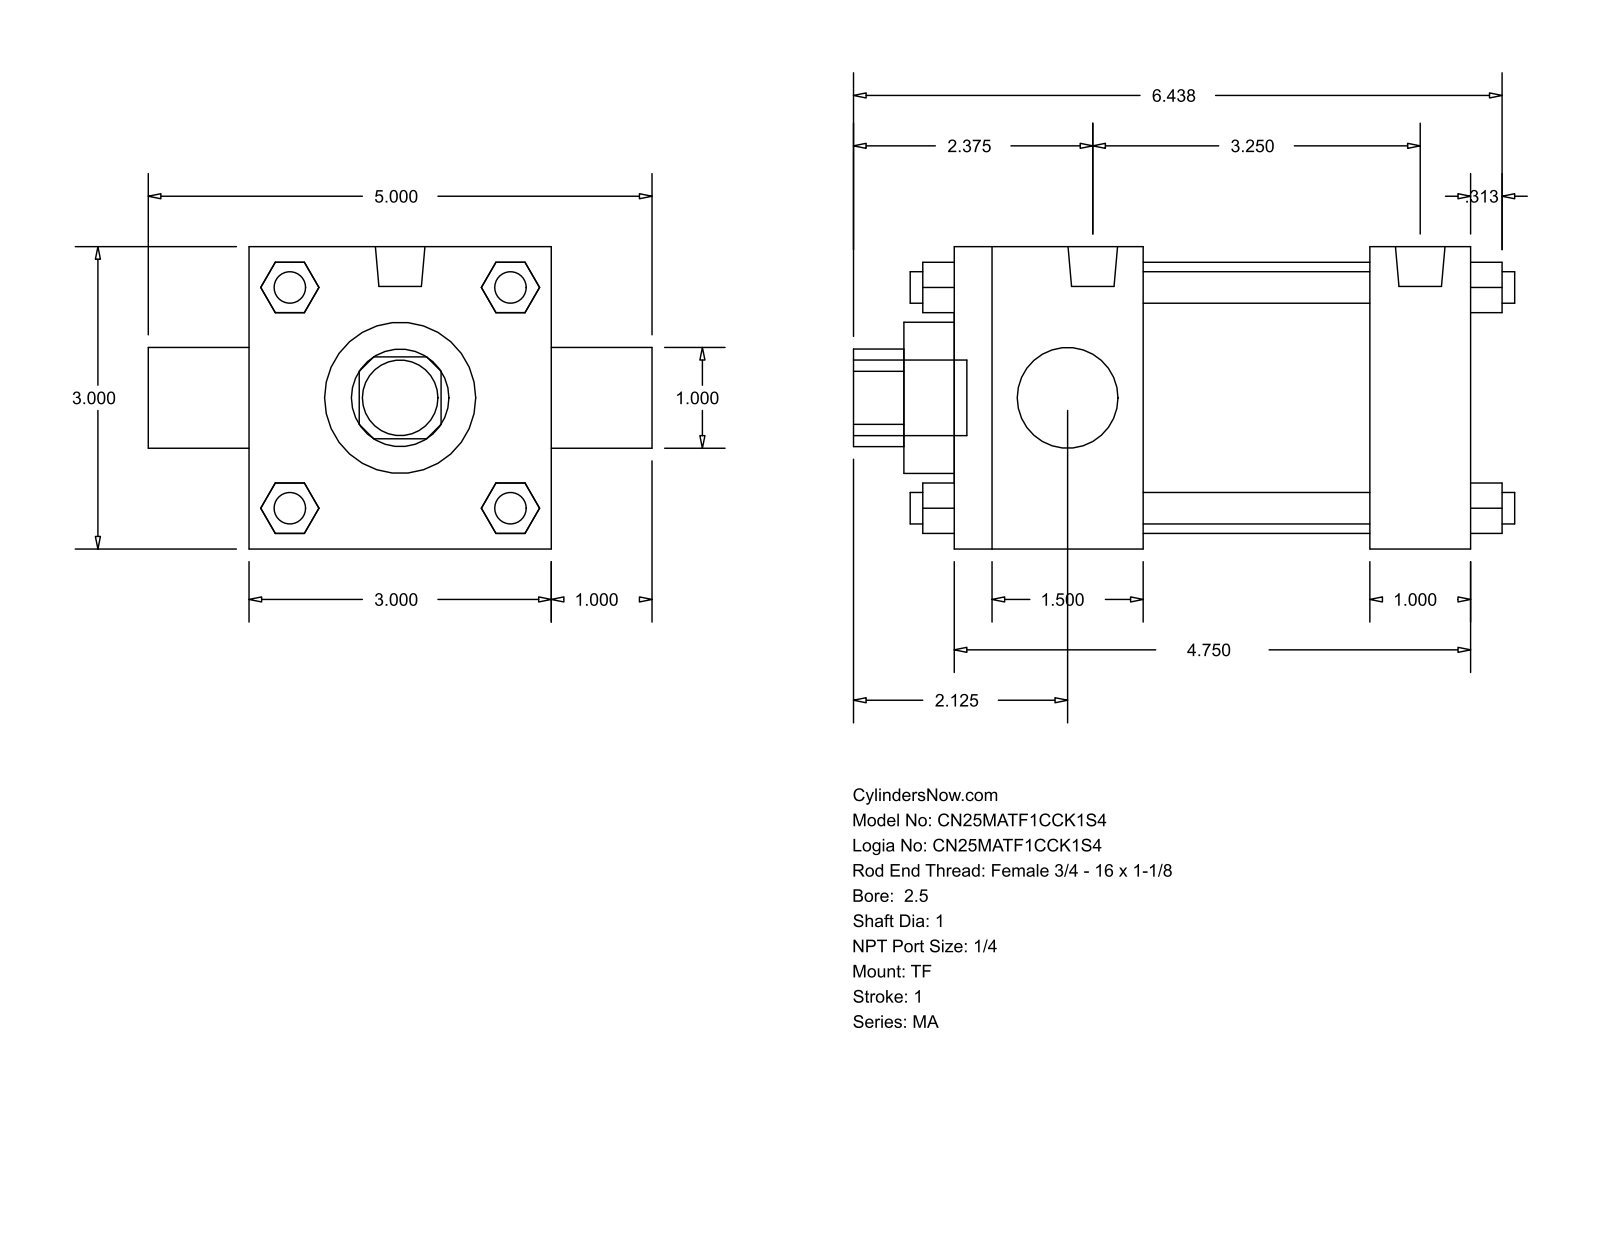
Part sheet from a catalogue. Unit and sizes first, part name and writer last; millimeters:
Units: millimetres
Overall size (bounding box): 166.69 × 127 × 76.2
Round holes (diameter × count): ⌀25.4 ×2, ⌀38.1 ×1, ⌀68.33 ×1
Round bosses / shafts (diameter × count): ⌀7.94 ×7, ⌀12.49 ×2, ⌀19.05 ×1
Partial cylindrical surfaces — rounded edges, fillets, slot ends (radius × count): R12.29 ×1
Main face-to-face distances: 76.2, 130.17, 12.7, 47.63, 104.78, 57.15, 82.54, 25.39, 25.4, 101.6
Bodies: 0 solids, 120 faces (92 planar, 28 cylindrical, 0 other)
Part name (STEP PRODUCT): MA_TF__0250_1
STEP written by: GSSL Pune (CONFIG_CONTROL_DESIGN)
